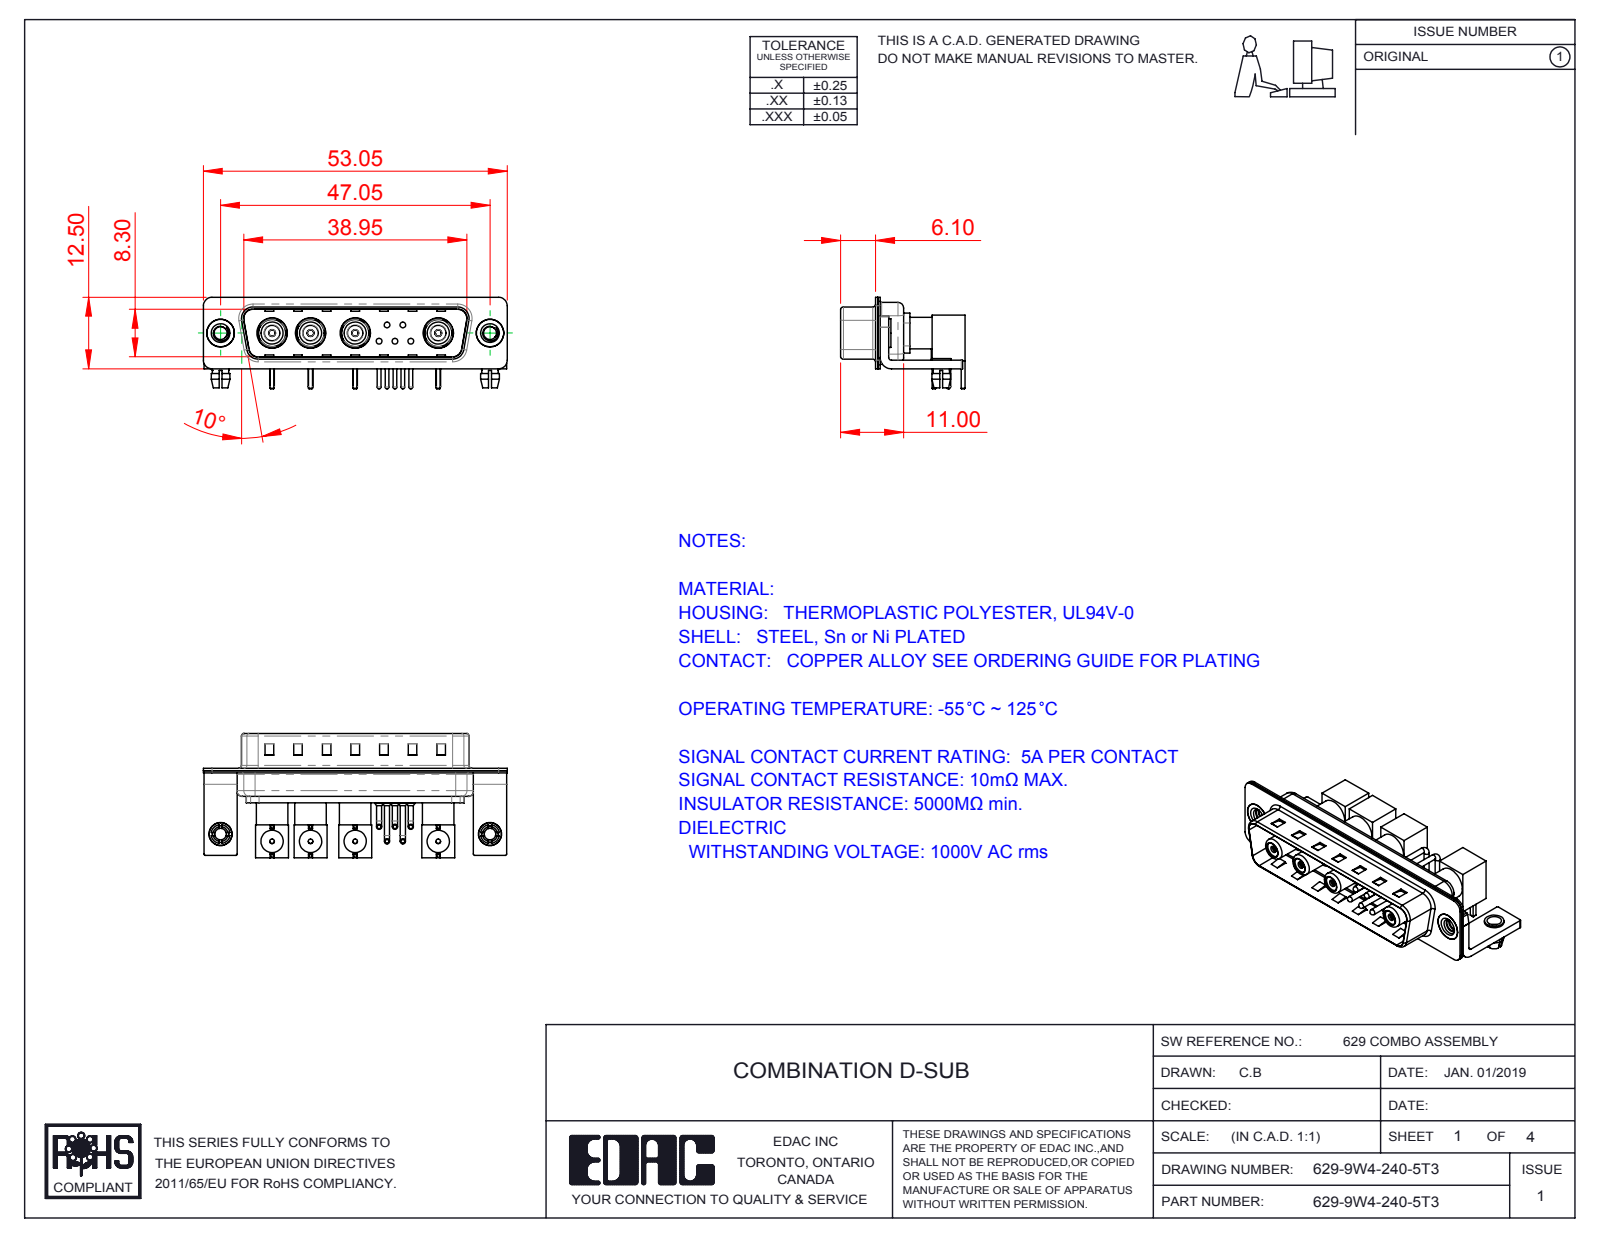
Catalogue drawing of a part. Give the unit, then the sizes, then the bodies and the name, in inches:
Units: inches
Overall size (bounding box): 2.089 × 0.855 × 0.63
Round holes (diameter × count): ⌀0.063 ×9, ⌀0.079 ×7, ⌀0.098 ×6, ⌀0.03 ×5, ⌀0.031 ×4, ⌀0.043 ×4, ⌀0.047 ×4, ⌀0.059 ×4, ⌀0.106 ×4, ⌀0.122 ×4, ⌀0.134 ×4, ⌀0.154 ×4
Round bosses / shafts (diameter × count): ⌀0.035 ×10, ⌀0.031 ×8, ⌀0.157 ×6, ⌀0.13 ×6, ⌀0.114 ×6, ⌀0.059 ×5, ⌀0.039 ×5, ⌀0.026 ×5
Partial cylindrical surfaces — rounded edges, fillets, slot ends (radius × count): R0.01 ×16, R0.059 ×16, R0.079 ×13, R0.02 ×9, R0.063 ×8, R0.04 ×5, R0.024 ×4, R0.026 ×4
Main face-to-face distances: 0.016, 0.031, 0.374, 0.059, 0.226, 0.358, 0.343, 0.055, 0.39, 0.014
Hole centre spacings: 0.571, 0.572, 0.265, 0.307, 0.878, 1.143, 0.124, 0.571
Volume: 0.256 in³ · Surface area: 17.71 in²
Bodies: 42 solids, 1666 faces (787 planar, 635 cylindrical, 244 other)
Part name (STEP PRODUCT): Insulator Socket; Co-Ax Jack Assy_RA; Insulator Socket 2; 629-9W4-240-5T3 (+8 more)
STEP written by: SolidWorks 2020 (CONFIG_CONTROL_DESIGN)
